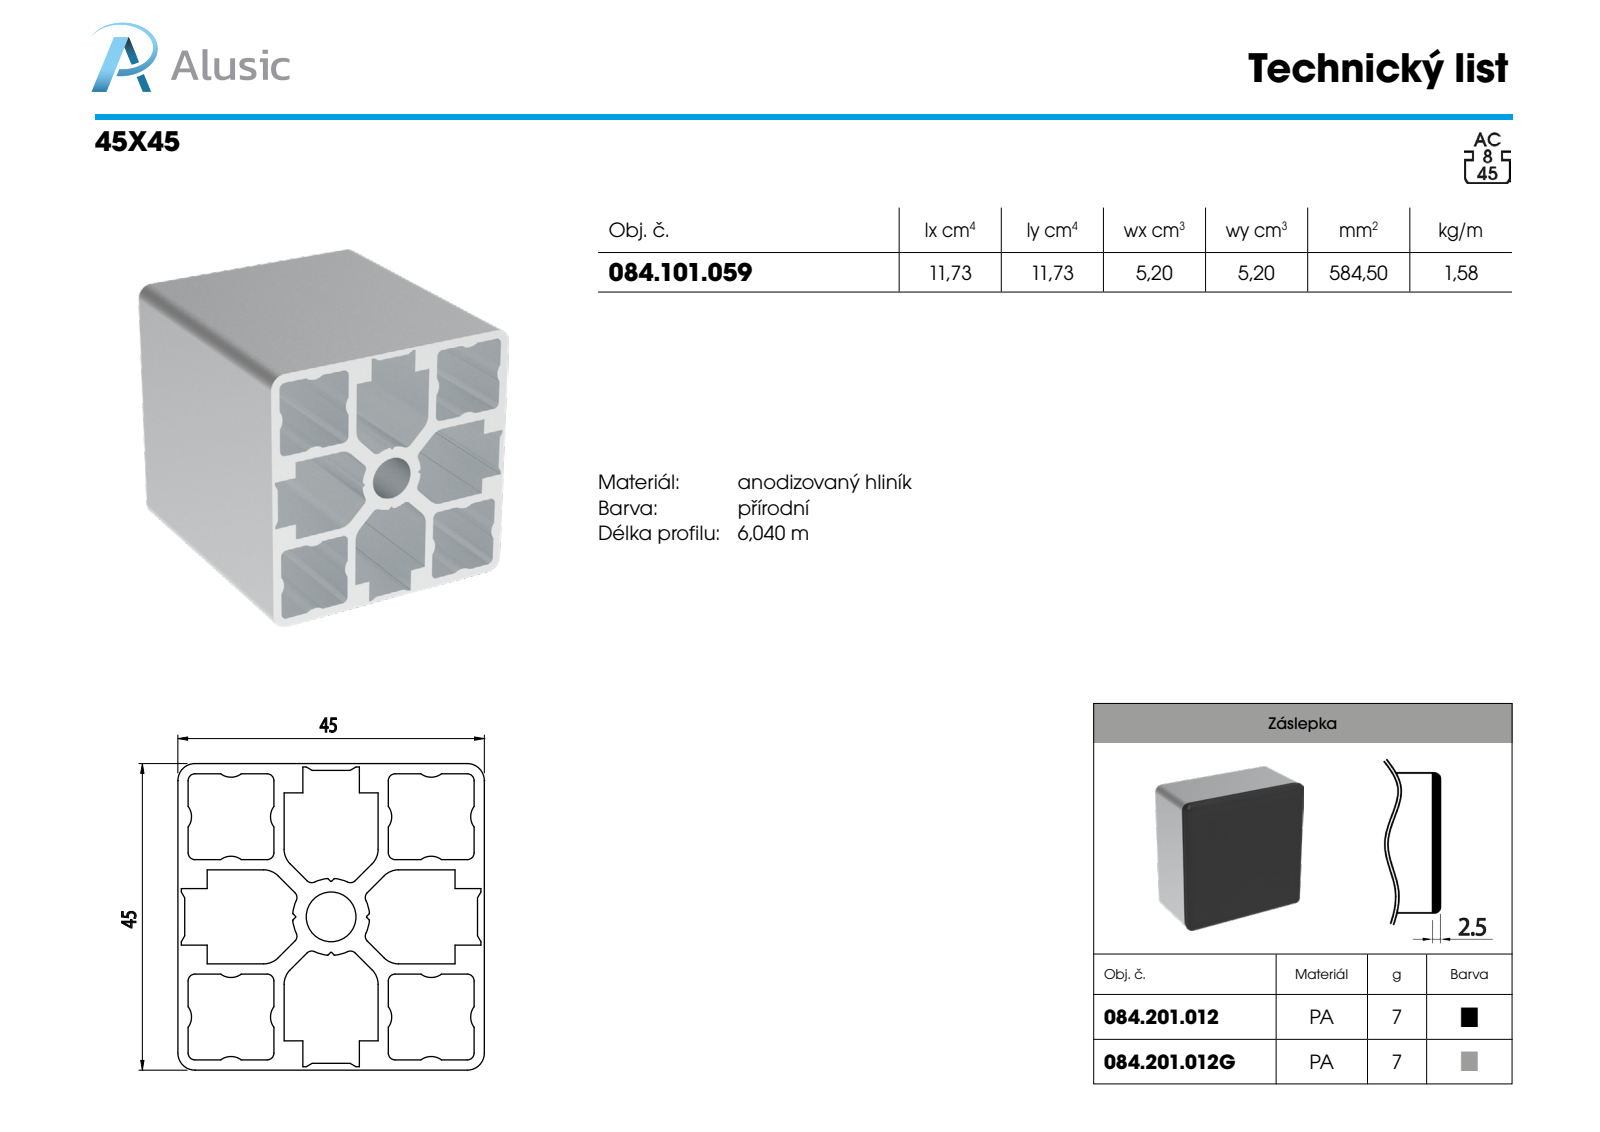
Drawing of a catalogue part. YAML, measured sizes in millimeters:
part_name: "084.101.059"
step_written_by: "SolidWorks 2018 (AUTOMOTIVE_DESIGN)"
units: millimeters
bodies: {solids: 1, faces: 181, planar: 98, cylindrical: 83, other: 0}
overall_size: [100, 45, 45]
volume: 58452
surface_area: 63951
round_holes:
  - {diameter: 7.3, count: 1}
partial_cylinders:
  - {radius: 1, count: 24}
  - {radius: 2.5, count: 20}
  - {radius: 0.1, count: 12}
  - {radius: 3, count: 8}
  - {radius: 5.65, count: 1}
face_to_face_distances: [29.4, 14.1, 1.5, 45, 15.6, 43.5, 30.9, 15.3, 27.9, 12.6]
